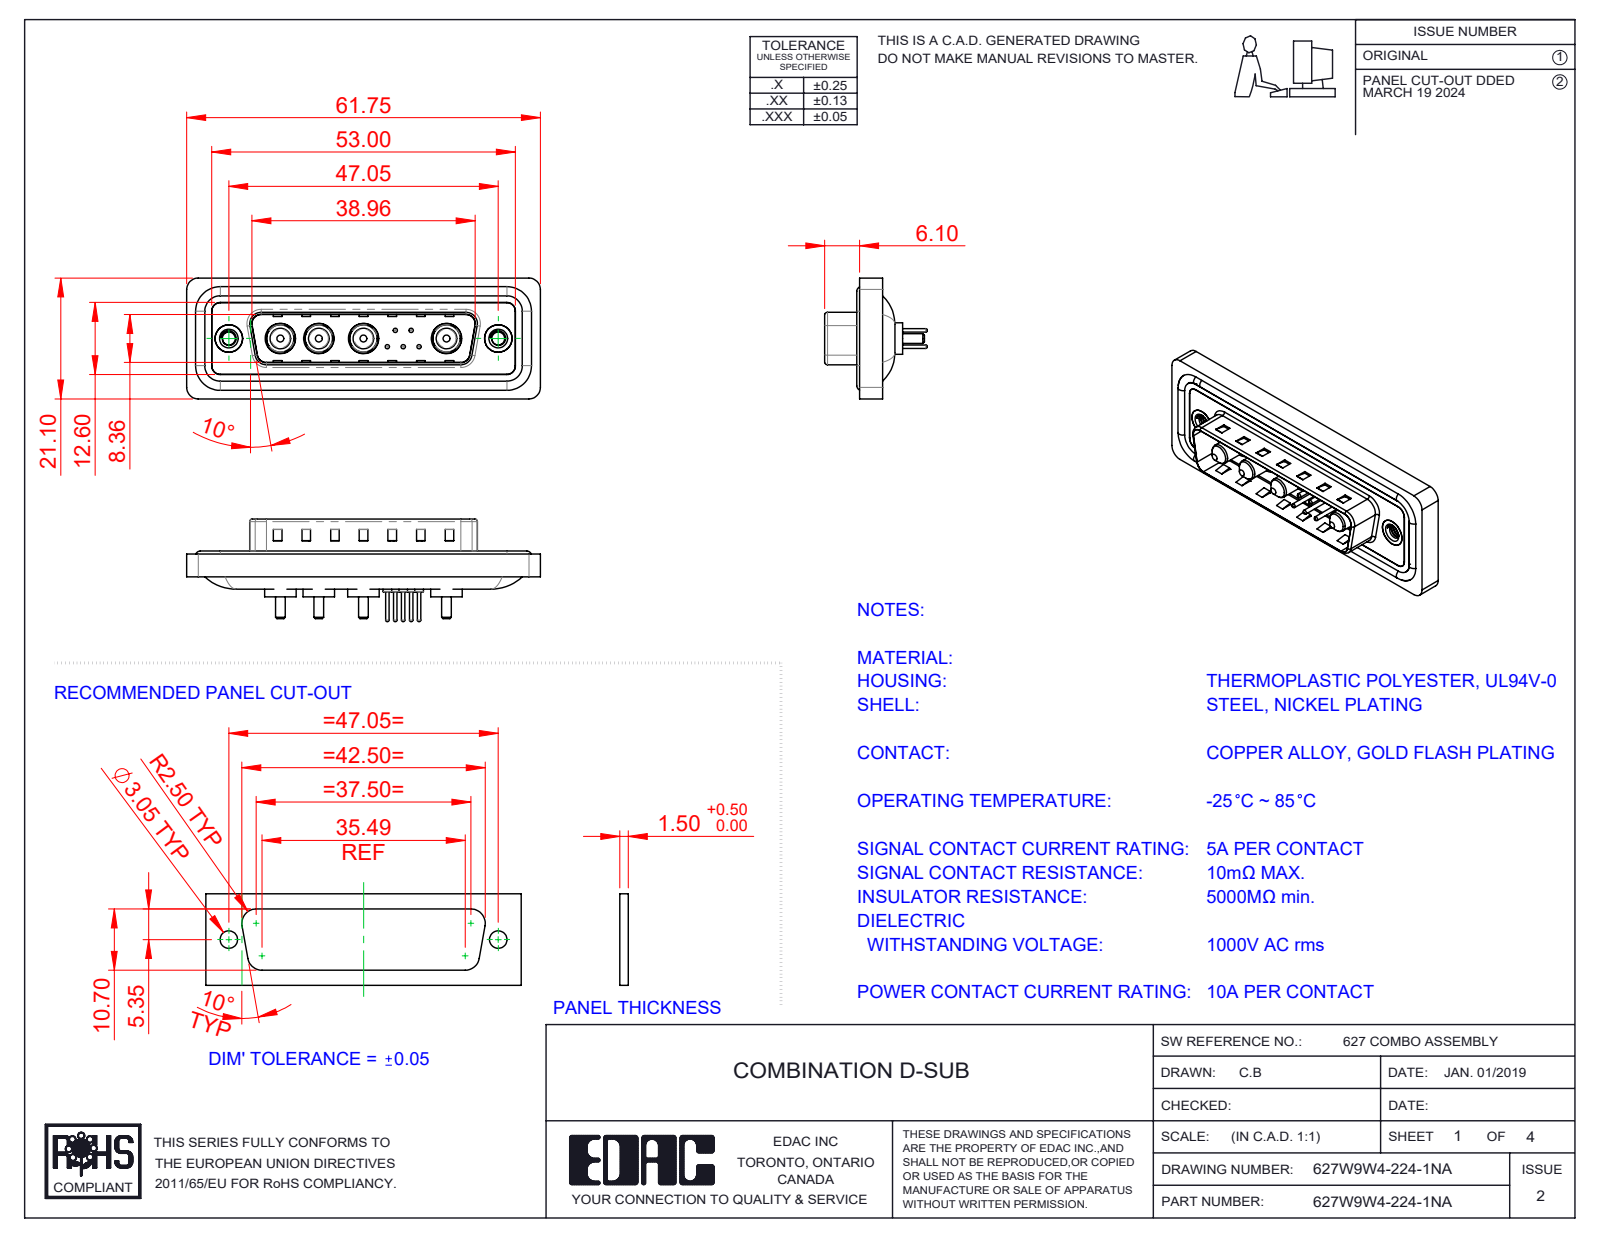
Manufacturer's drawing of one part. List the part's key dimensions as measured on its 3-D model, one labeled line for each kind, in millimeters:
Part name (STEP PRODUCT): 627Combo Waterproof Housing_25 Contacts; Power Pin_10A S; 627Combo Shell Rear_25 Contacts; 627Combo Housing_9W4 (+5 more)
STEP written by: SolidWorks 2023 (CONFIG_CONTROL_DESIGN)
Units: millimetres
Bodies: 20 solids, 822 faces (284 planar, 336 cylindrical, 202 other)
Overall size (bounding box): 61.75 × 21.1 × 17.9
Volume: 7 347 mm³ · Surface area: 11 782 mm²
Round holes (diameter × count): ⌀0.75 ×5, ⌀1.6 ×5, ⌀2 ×5, ⌀4.85 ×4, ⌀5.3 ×4, ⌀2.26 ×2, ⌀4 ×2, ⌀4.8 ×2, ⌀5 ×2
Round bosses / shafts (diameter × count): ⌀1.5 ×5, ⌀0.6 ×5, ⌀5.5 ×4, ⌀5.2 ×4, ⌀4.75 ×4, ⌀3.75 ×4, ⌀3.6 ×4, ⌀1.7 ×4
Partial cylindrical surfaces — rounded edges, fillets, slot ends (radius × count): R1.5 ×22, R2 ×18, R0.5 ×8, R1.6 ×8, R0.25 ×4, R0.6 ×4, R0.65 ×4, R0.9 ×4
Main face-to-face distances: 0.4, 1.5, 1.1, 0.5, 3.1, 1.6, 2.9, 0.82, 9.58, 5.65
Hole centre spacings: 3.16, 2.77, 5.04, 14.51, 2.78, 4.4, 4.41, 5
